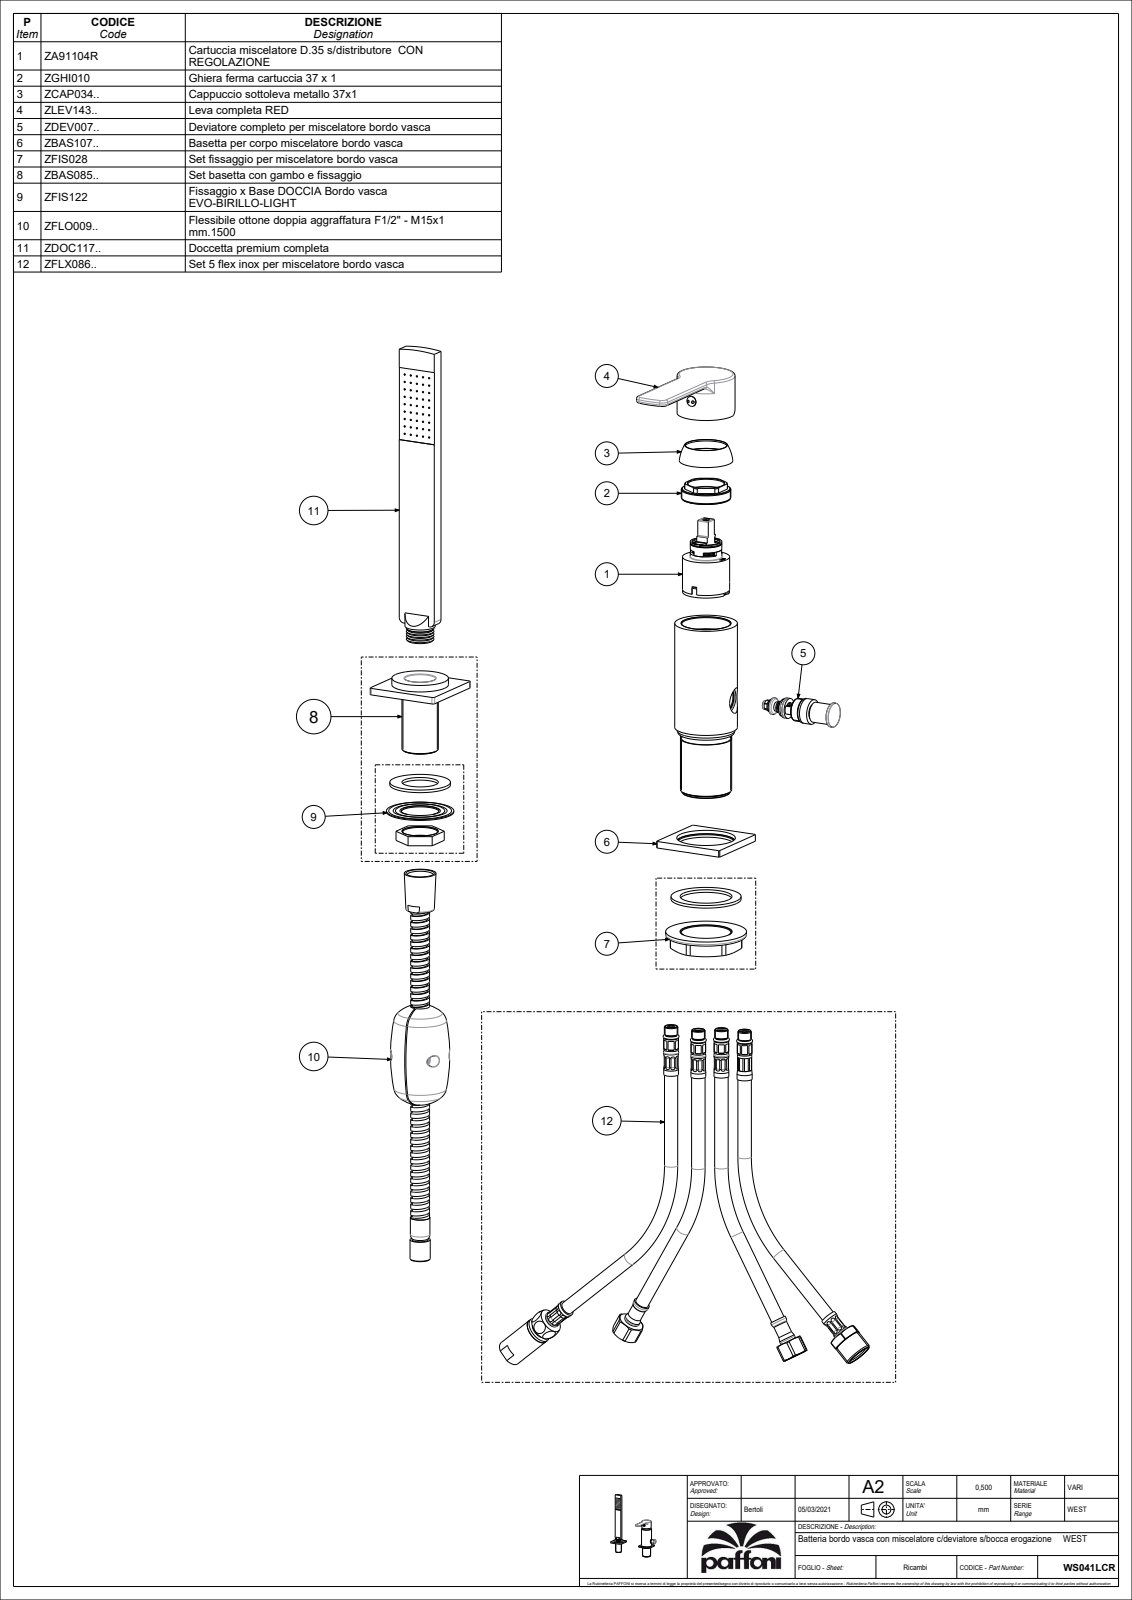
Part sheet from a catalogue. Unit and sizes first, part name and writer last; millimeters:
Units: millimetres
Overall size (bounding box): 228 × 221.46 × 112.5
Round holes (diameter × count): ⌀7 ×6, ⌀3.3 ×2, ⌀4 ×2, ⌀4.5 ×2, ⌀3 ×1, ⌀3.1 ×1, ⌀4.3 ×1, ⌀5 ×1, ⌀6 ×1, ⌀7.2 ×1, ⌀9 ×1, ⌀9.5 ×1
Round bosses / shafts (diameter × count): ⌀2 ×11, ⌀46.5 ×1, ⌀44.2 ×1, ⌀43 ×1, ⌀42.5 ×1, ⌀42 ×1, ⌀38 ×1, ⌀35 ×1
Partial cylindrical surfaces — rounded edges, fillets, slot ends (radius × count): R0.5 ×66, R0.15 ×11, R1.5 ×8, R0.3 ×4, R1 ×2, R4 ×2, R5 ×2, R10 ×2
Main face-to-face distances: 10, 5, 3, 30, 117.1, 112.1, 1, 4.5, 9.8, 121.6
Hole centre spacings: 3, 8.6, 10.63, 14, 14.32, 12.5, 59.31, 143.09
Volume: 234 257 mm³ · Surface area: 99 527 mm²
Bodies: 4 solids, 1588 faces (915 planar, 396 cylindrical, 277 other)
Part name (STEP PRODUCT): WS041LCR
STEP written by: CREO PARAMETRIC BY PTC INC, 2020044 (CONFIG_CONTROL_DESIGN)
